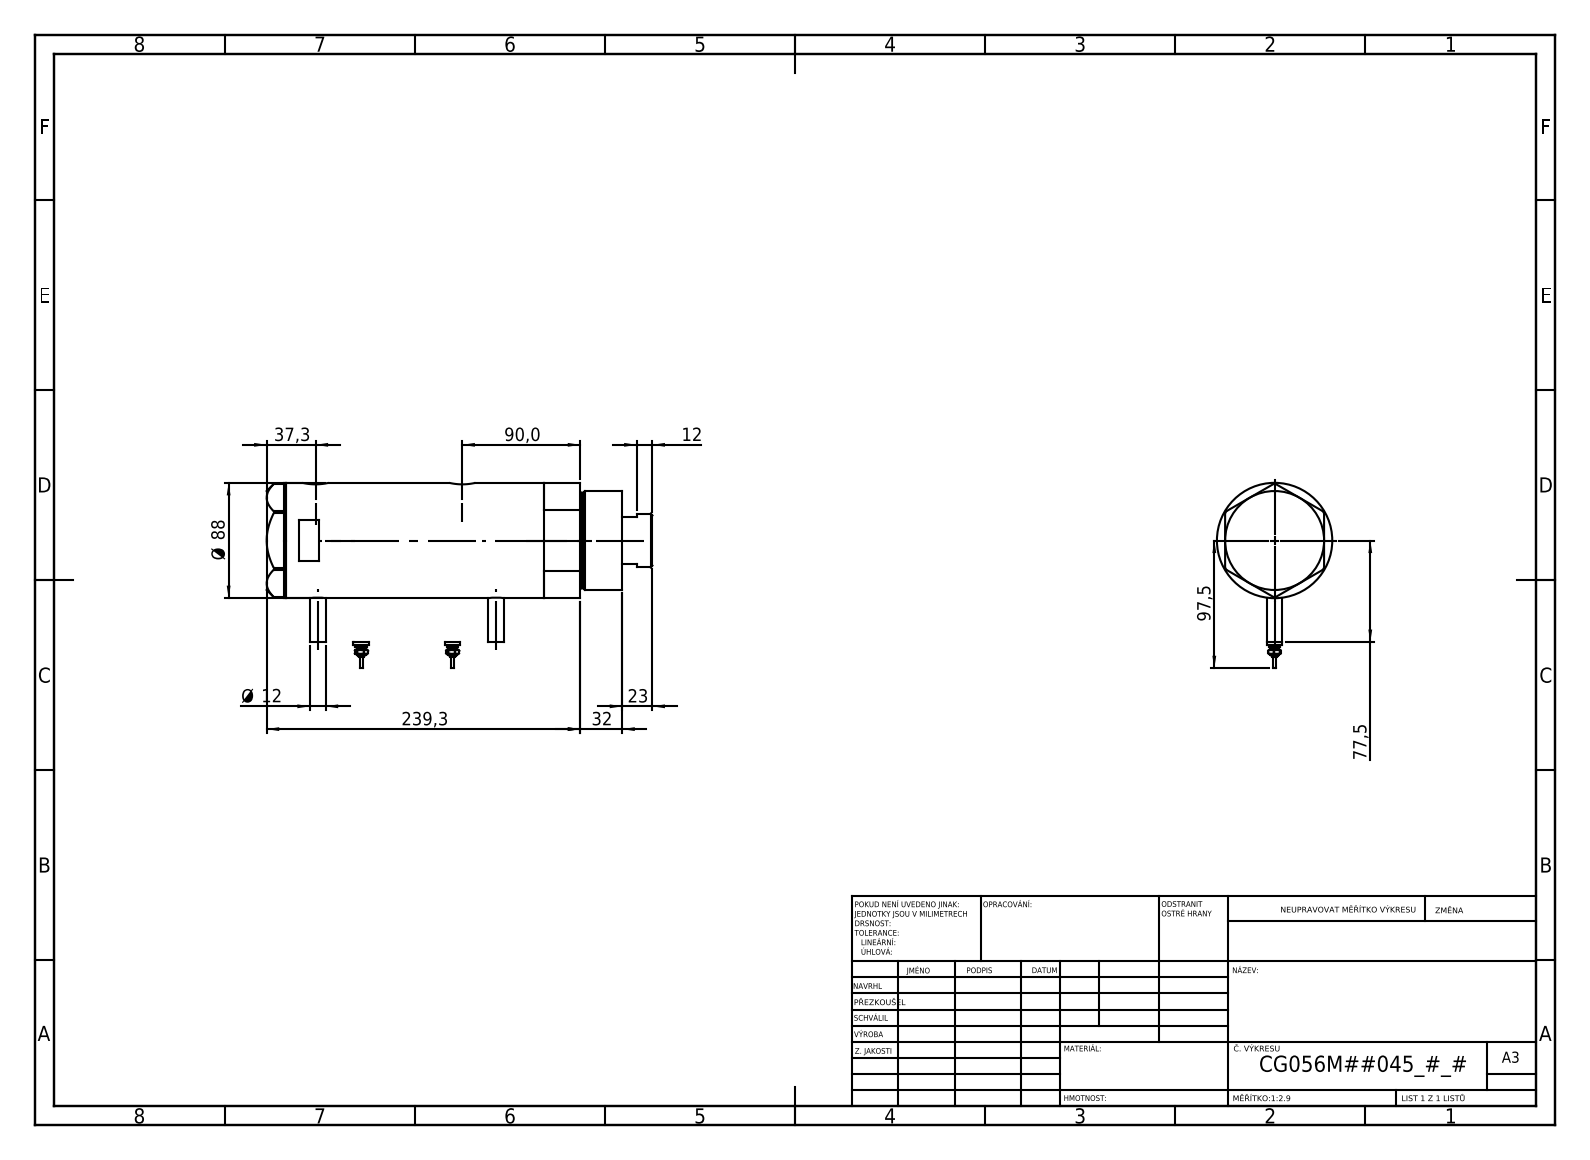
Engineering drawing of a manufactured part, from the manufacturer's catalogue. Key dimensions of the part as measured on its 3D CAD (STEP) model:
Part name (STEP PRODUCT): V270CG_FRONT; Switch; V270CG_MIDDLE; V270CG_VC (+1 more)
STEP written by: SolidWorks 2019 (CONFIG_CONTROL_DESIGN)
Units: millimetres
Bodies: 6 solids, 213 faces (80 planar, 69 cylindrical, 64 other)
Overall size (bounding box): 294.3 × 141.5 × 88
Volume: 1 547 000 mm³ · Surface area: 224 809 mm²
Round holes (diameter × count): ⌀12.5 ×2, ⌀13.16 ×2, ⌀20 ×2, ⌀14.5 ×1, ⌀42 ×1, ⌀43.5 ×1, ⌀56 ×1, ⌀60 ×1, ⌀80 ×1
Round bosses / shafts (diameter × count): ⌀12 ×4, ⌀9 ×2, ⌀7 ×2, ⌀4.5 ×2, ⌀2.5 ×2, ⌀88 ×1, ⌀75 ×1, ⌀73 ×1
Main face-to-face distances: 134.4, 26, 108.4, 15, 41, 149.4, 256.3, 271.3, 230.3, 121.9
Hole centre spacings: 1.7, 25.8, 110.3, 112, 136.1, 137.8
